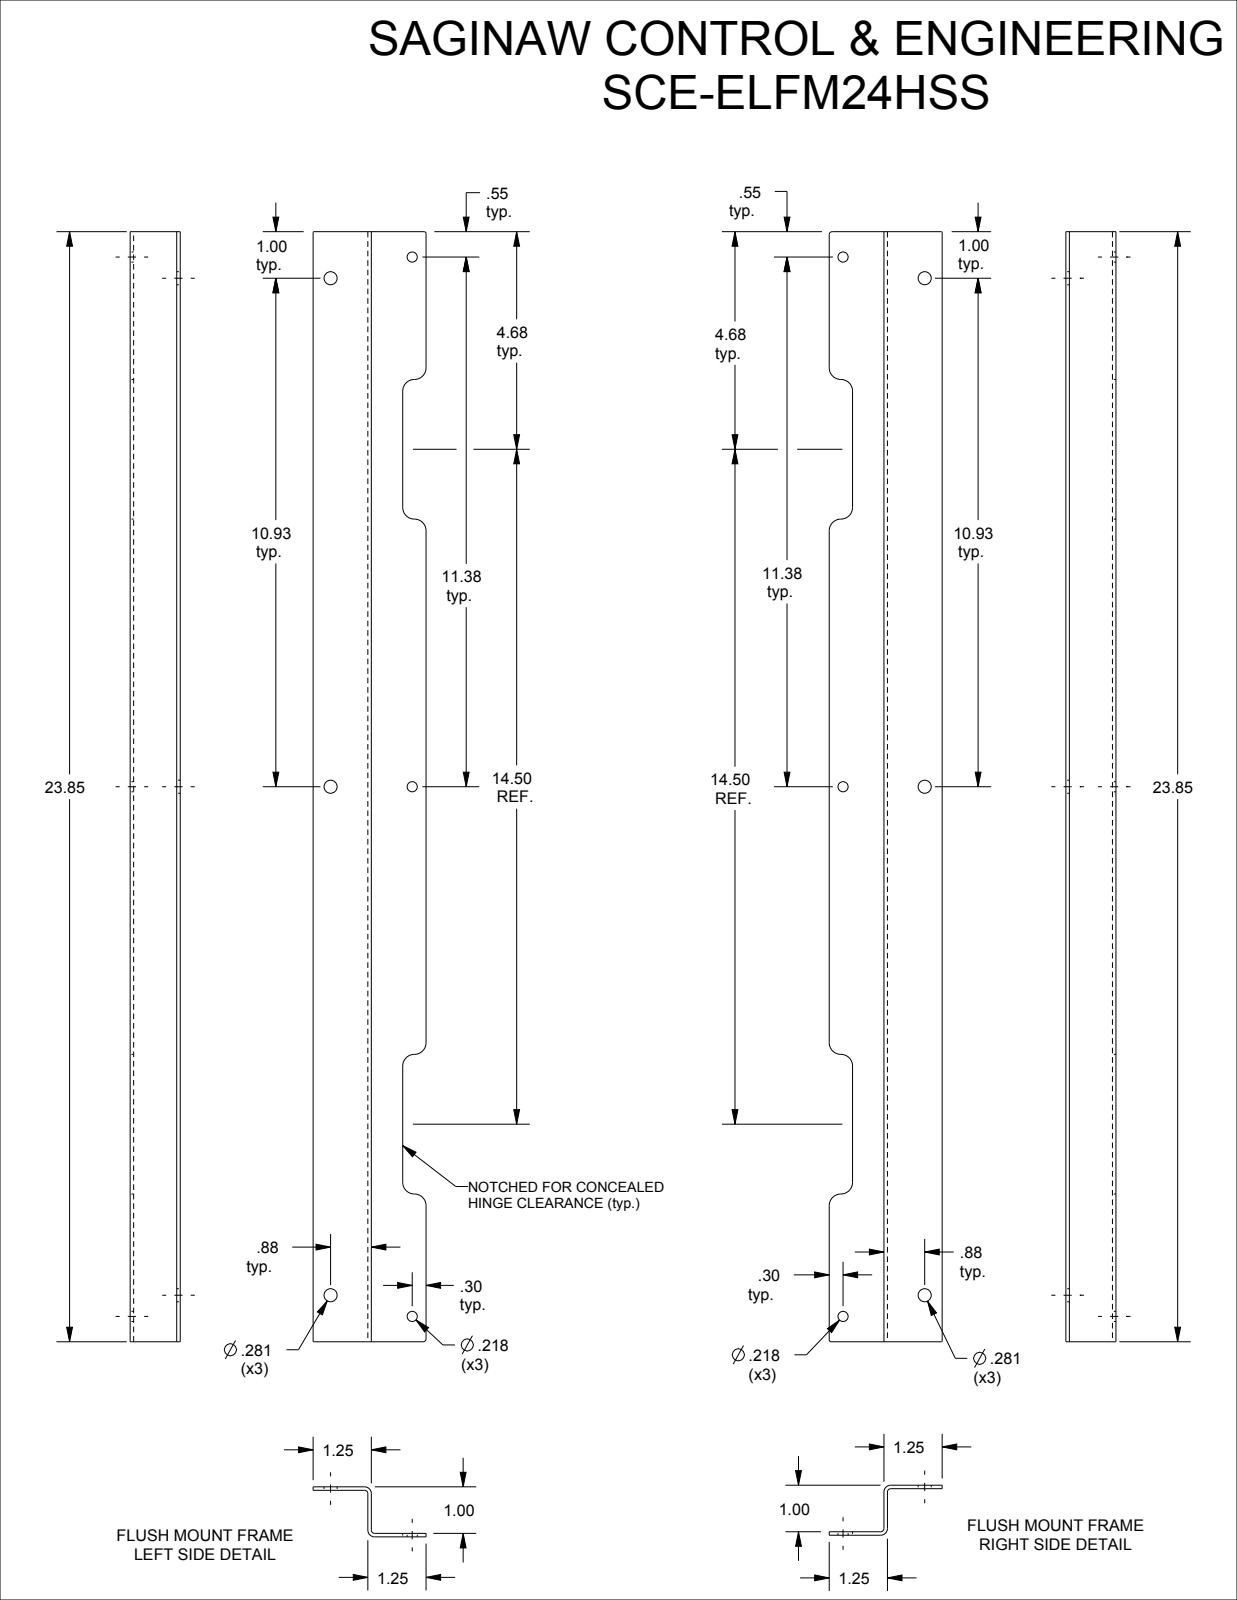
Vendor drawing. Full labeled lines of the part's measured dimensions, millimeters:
Part name (STEP PRODUCT): SCE-ELFM24H
STEP written by: SolidWorks 2019 (CONFIG_CONTROL_DESIGN)
Units: millimetres
Bodies: 2 solids, 80 faces (36 planar, 44 cylindrical, 0 other)
Overall size (bounding box): 685.8 × 605.8 × 27.3
Volume: 188 300 mm³ · Surface area: 203 400 mm²
Round holes (diameter × count): ⌀5.5 ×6, ⌀7.1 ×6
Partial cylindrical surfaces — rounded edges, fillets, slot ends (radius × count): R6.4 ×16, R0.4 ×4, R1.3 ×4, R3.2 ×4, R1 ×2, R1.6 ×2
Main face-to-face distances: 1.9, 1.9, 25.3, 27.3, 23.4, 25.3, 624.2, 626.1, 622.3, 624.2
Hole centre spacings: 46.1, 277.5, 281.1, 289.1, 292.5, 568.3, 622.3, 645.9
